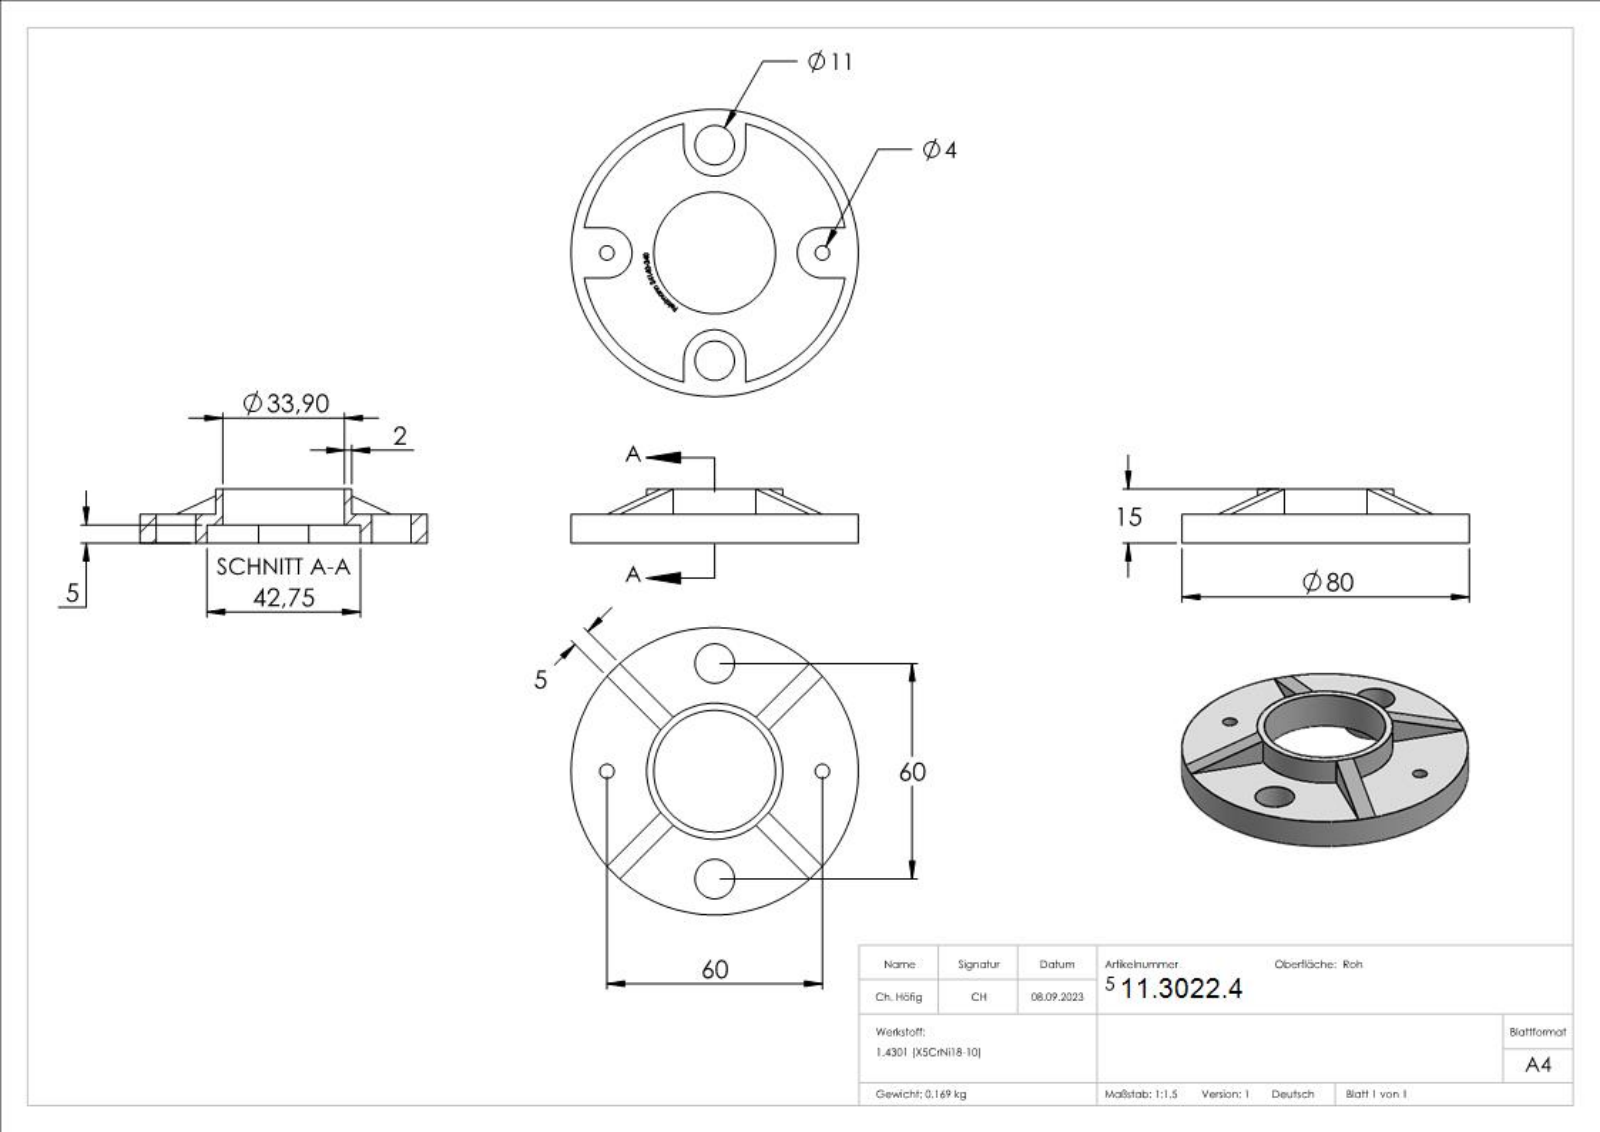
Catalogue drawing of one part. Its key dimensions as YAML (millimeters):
part_name: "54140-240"
step_written_by: "SolidWorks 2018 (CONFIG_CONTROL_DESIGN)"
units: millimeters
bodies: {solids: 1, faces: 269, planar: 171, cylindrical: 18, other: 80}
overall_size: [80, 80, 15]
volume: 21358
surface_area: 14549
round_holes:
  - {diameter: 4, count: 2}
  - {diameter: 11, count: 2}
  - {diameter: 33.9, count: 1}
round_bosses_or_shafts:
  - {diameter: 80, count: 1}
  - {diameter: 37.9, count: 1}
partial_cylinders:
  - {radius: 7, count: 2}
  - {radius: 8.62, count: 2}
  - {radius: 37, count: 1}
face_to_face_distances: [3, 5, 8, 15, 10, 7, 14, 17.26, 5.1, 2.9]
hole_center_spacings: [30, 42.43, 60]
